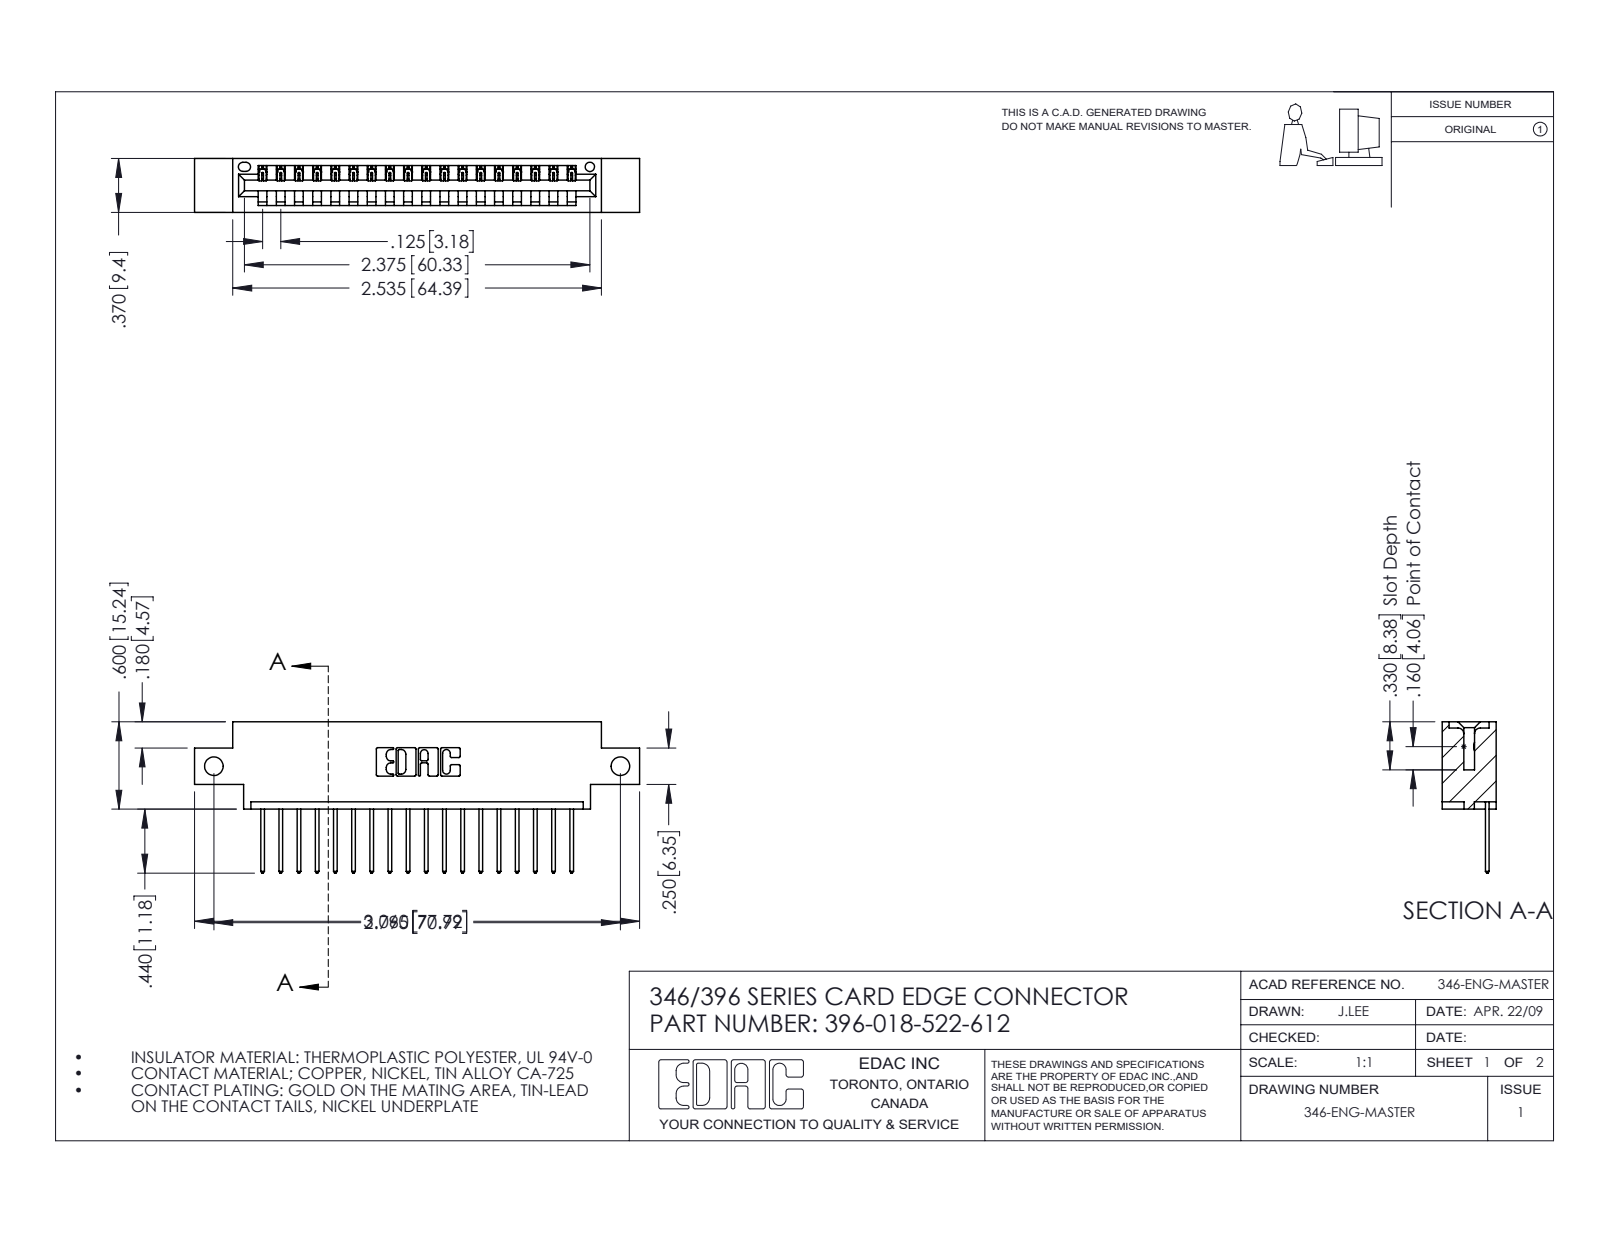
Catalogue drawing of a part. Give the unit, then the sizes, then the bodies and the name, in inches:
Units: inches
Overall size (bounding box): 3.06 × 1.04 × 0.37
Round holes (diameter × count): ⌀0.128 ×2, ⌀0.064 ×1
Partial cylindrical surfaces — rounded edges, fillets, slot ends (radius × count): R0.006 ×36, R0.01 ×36, R0.01 ×22, R0.007 ×6, R0.031 ×6, R0.026 ×3, R0.031 ×2, R0.04 ×2
Main face-to-face distances: 0.048, 0.322, 0.37, 0.25, 0.072, 0.298, 0.025, 0.148, 0.222, 0.1
Hole centre spacings: 2.795
Volume: 0.429 in³ · Surface area: 13.35 in²
Bodies: 19 solids, 1170 faces (800 planar, 370 cylindrical, 0 other)
Part name (STEP PRODUCT): 345-292-001_345-293-122; 396-018-522-612; 346 Part_0.170 Offset - Side Mount
STEP written by: SolidWorks 2016 (CONFIG_CONTROL_DESIGN)
